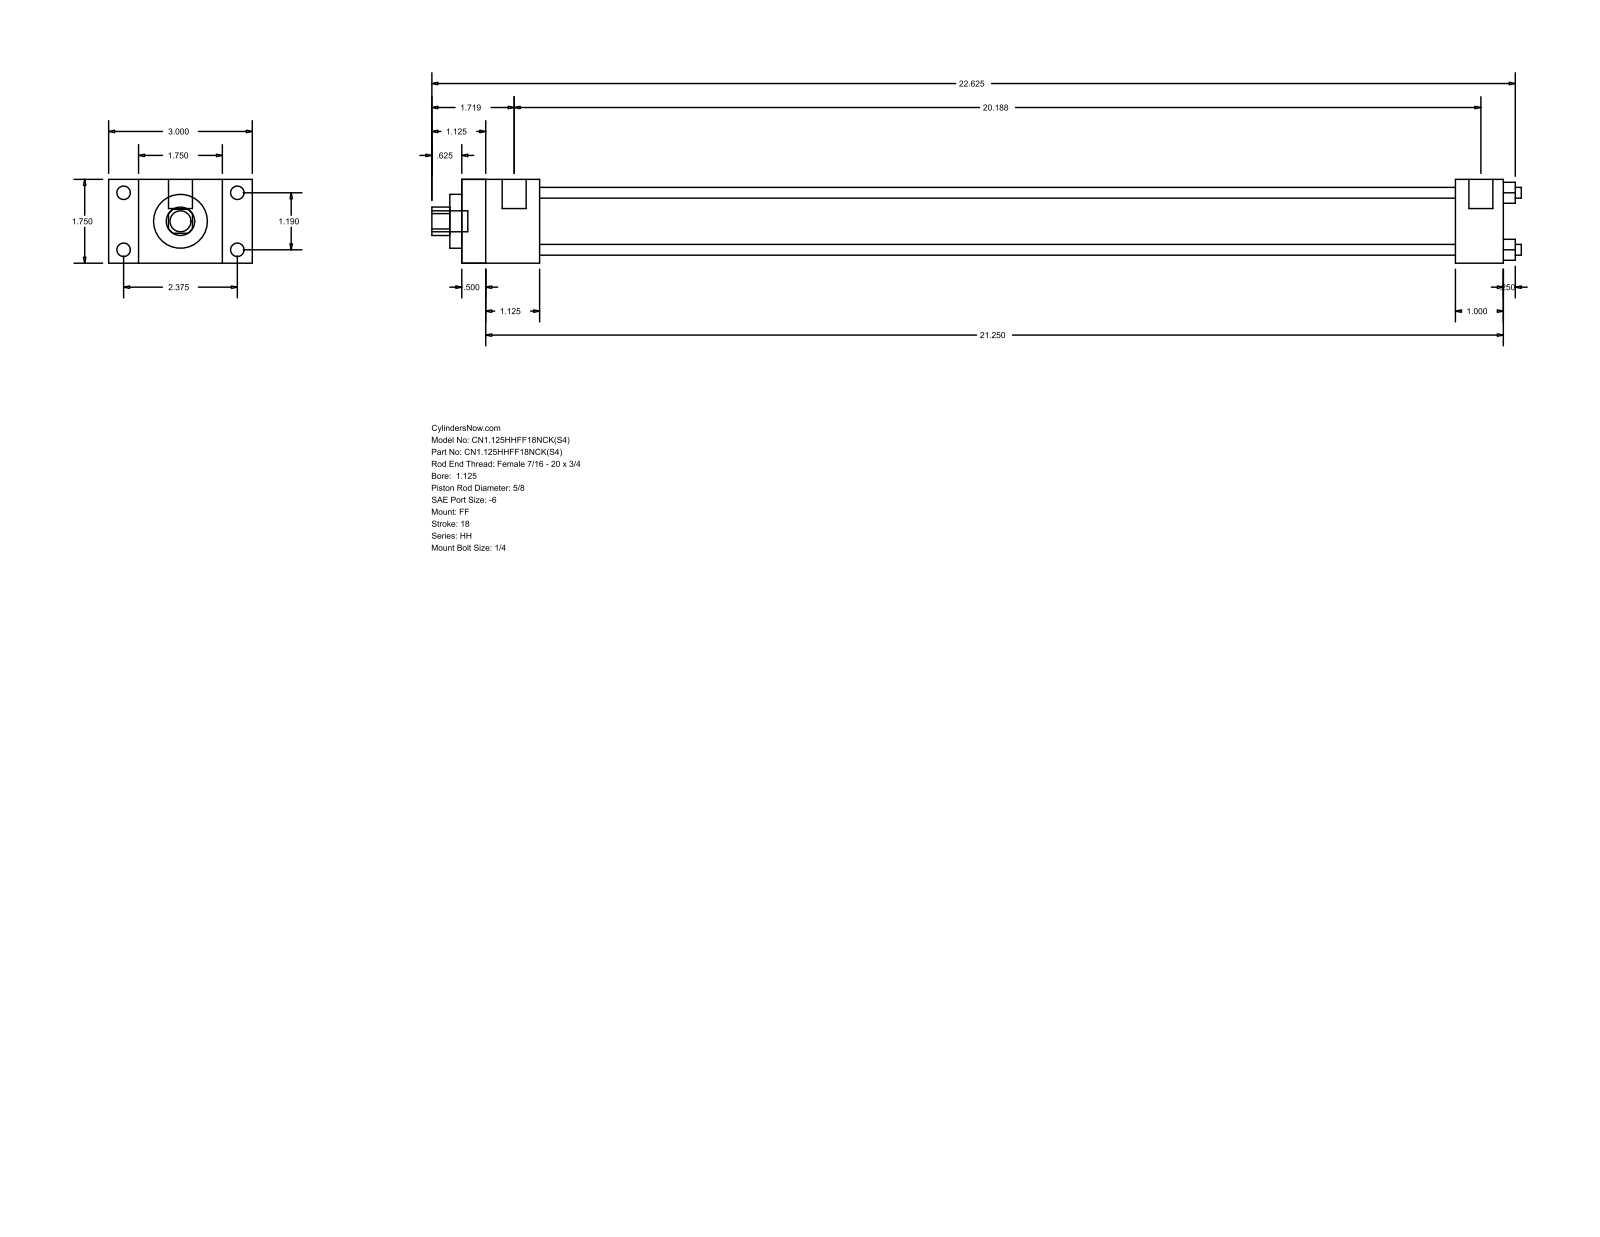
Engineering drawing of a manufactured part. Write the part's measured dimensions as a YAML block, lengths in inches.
part_name: "HH_FF__0112_0.625"
step_written_by: "GSSL Pune (CONFIG_CONTROL_DESIGN)"
units: inches
bodies: {solids: 0, faces: 92, planar: 64, cylindrical: 28, other: 0}
overall_size: [22.75, 3, 1.75]
round_holes:
  - {diameter: 0.225, count: 4}
  - {diameter: 0.625, count: 1}
  - {diameter: 1.125, count: 1}
  - {diameter: 1.375, count: 1}
round_bosses_or_shafts:
  - {diameter: 0.281, count: 4}
  - {diameter: 0.219, count: 4}
  - {diameter: 0.5, count: 2}
  - {diameter: 0.437, count: 1}
partial_cylinders:
  - {radius: 0.297, count: 1}
face_to_face_distances: [1.75, 21.75, 0.625, 0.5, 21.25, 2.375, 1.125, 1.625, 20.75, 20.25]
hole_center_spacings: [0.841, 1.19, 1.683]
